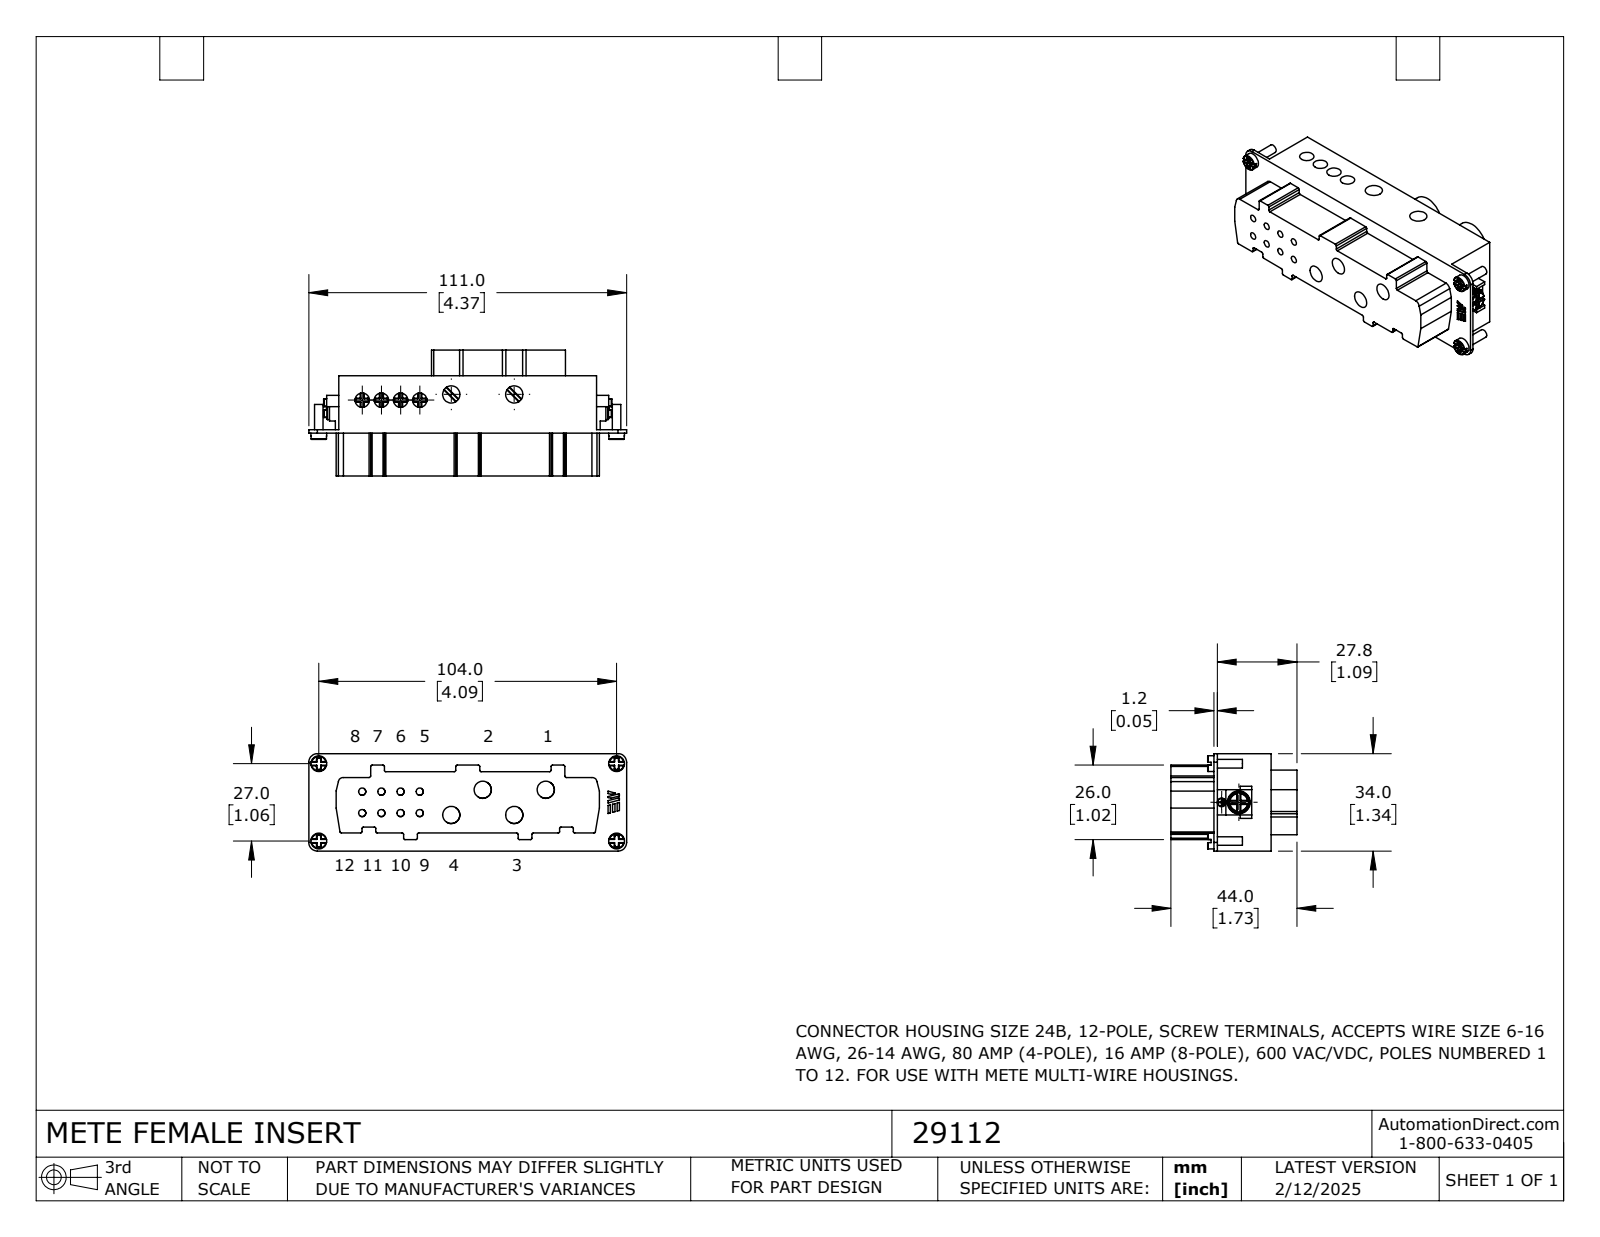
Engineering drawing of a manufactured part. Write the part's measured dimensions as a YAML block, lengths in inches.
part_name: "29112"
step_written_by: "SolidWorks 2024 (CONFIG_CONTROL_DESIGN)"
units: inches
bodies: {solids: 1, faces: 1087, planar: 491, cylindrical: 372, other: 224}
overall_size: [4.37, 1.732, 1.339]
volume: 5.681
surface_area: 35.44
round_holes:
  - {diameter: 0.098, count: 8}
  - {diameter: 0.236, count: 8}
  - {diameter: 0.197, count: 4}
  - {diameter: 0.315, count: 4}
  - {diameter: 0.118, count: 1}
round_bosses_or_shafts:
  - {diameter: 0.217, count: 4}
  - {diameter: 0.118, count: 4}
  - {diameter: 0.315, count: 1}
  - {diameter: 0.261, count: 1}
  - {diameter: 0.11, count: 1}
partial_cylinders:
  - {radius: 0.008, count: 88}
  - {radius: 0.012, count: 16}
  - {radius: 0.019, count: 10}
  - {radius: 0.02, count: 10}
  - {radius: 0.02, count: 6}
  - {radius: 0.047, count: 6}
  - {radius: 0.02, count: 4}
  - {radius: 0.118, count: 4}
face_to_face_distances: [0.591, 1.378, 0.787, 0.248, 1.09, 1.339, 0.047, 0.354, 0.842, 0.638]
hole_center_spacings: [0.264, 0.396, 0.528, 0.295, 0.605, 0.866, 0.433, 0.555]
